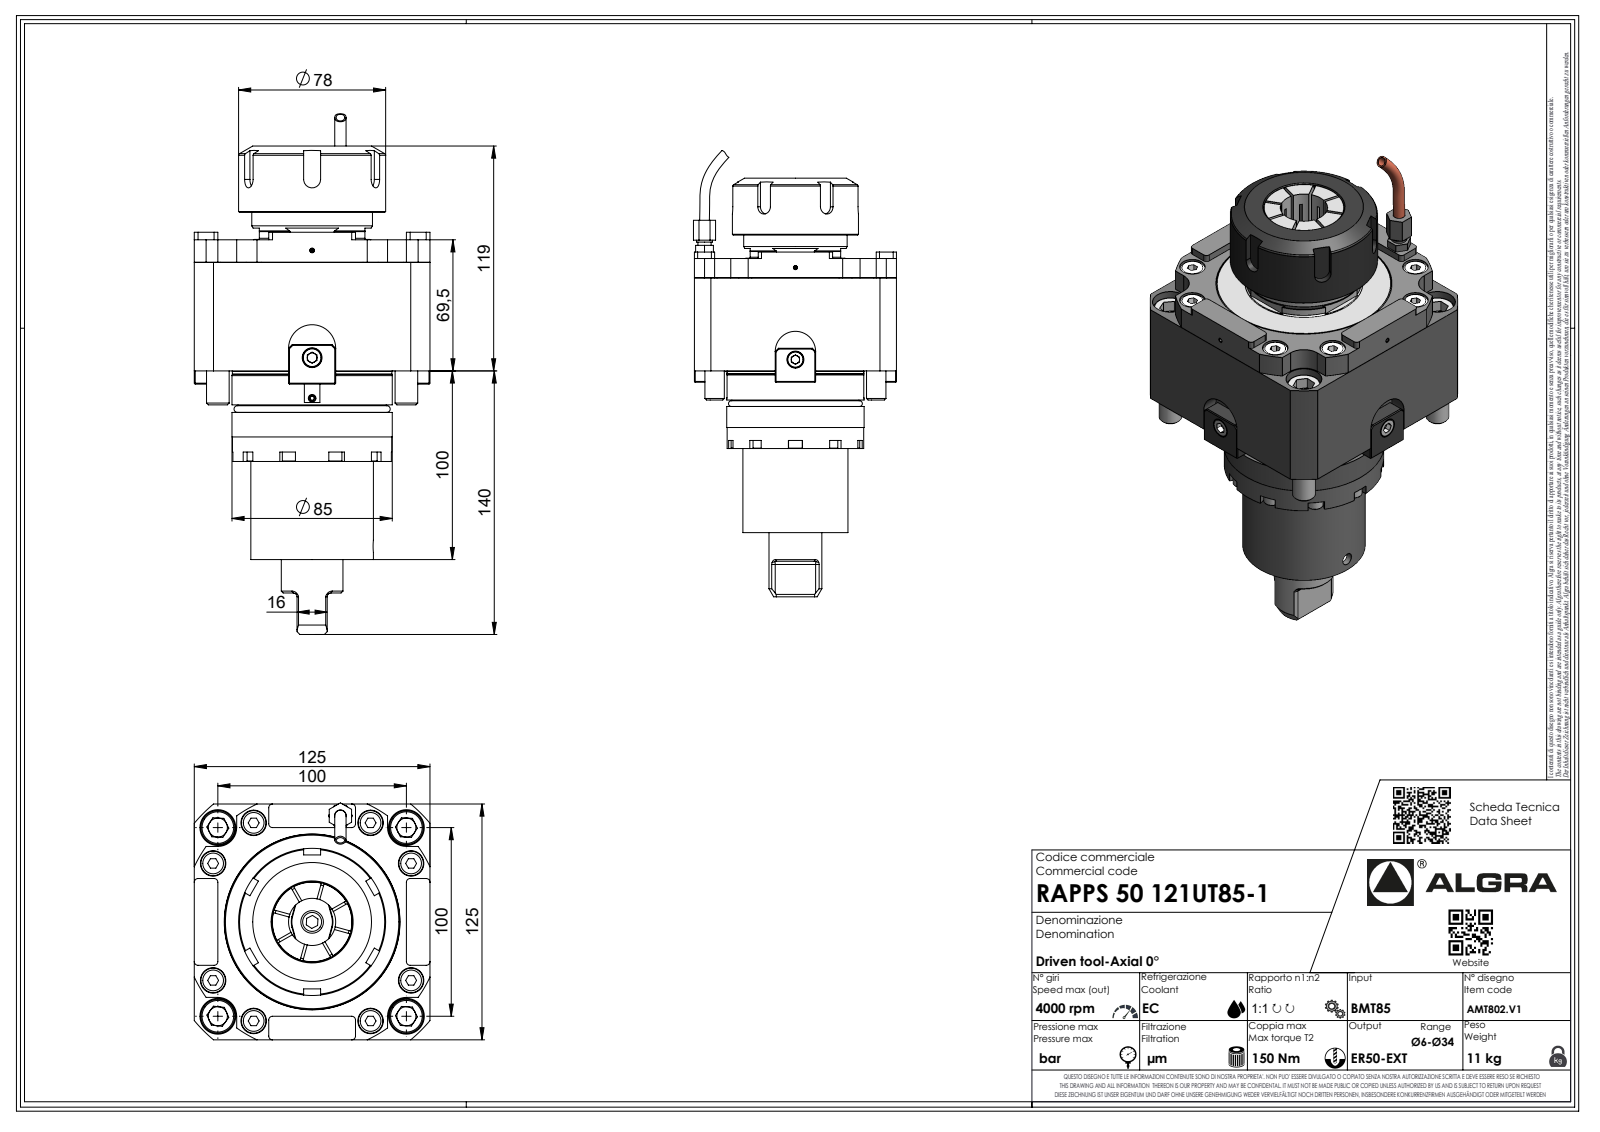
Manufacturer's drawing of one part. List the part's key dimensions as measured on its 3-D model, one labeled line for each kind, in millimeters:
Part name (STEP PRODUCT): RAPPS50121UT85-1
STEP written by: SolidWorks 2023 (AUTOMOTIVE_DESIGN)
Units: millimetres
Bodies: 1 solid, 581 faces (368 planar, 93 cylindrical, 120 other)
Overall size (bounding box): 258.9 × 125 × 125
Volume: 1 740 000 mm³ · Surface area: 112 688 mm²
Round holes (diameter × count): ⌀2.1 ×1
Round bosses / shafts (diameter × count): ⌀12 ×3, ⌀85 ×1, ⌀84.5 ×1, ⌀78 ×1, ⌀65 ×1, ⌀64 ×1, ⌀32.7 ×1, ⌀6.37 ×1
Partial cylindrical surfaces — rounded edges, fillets, slot ends (radius × count): R2 ×22, R4.35 ×10, R0.33 ×7, R0.52 ×7, R3.7 ×7, R10 ×4, R4.5 ×3, R0.21 ×1
Main face-to-face distances: 125, 69.4, 69.5, 119.2, 49.8, 49.7, 100, 12, 169.4, 169.5
